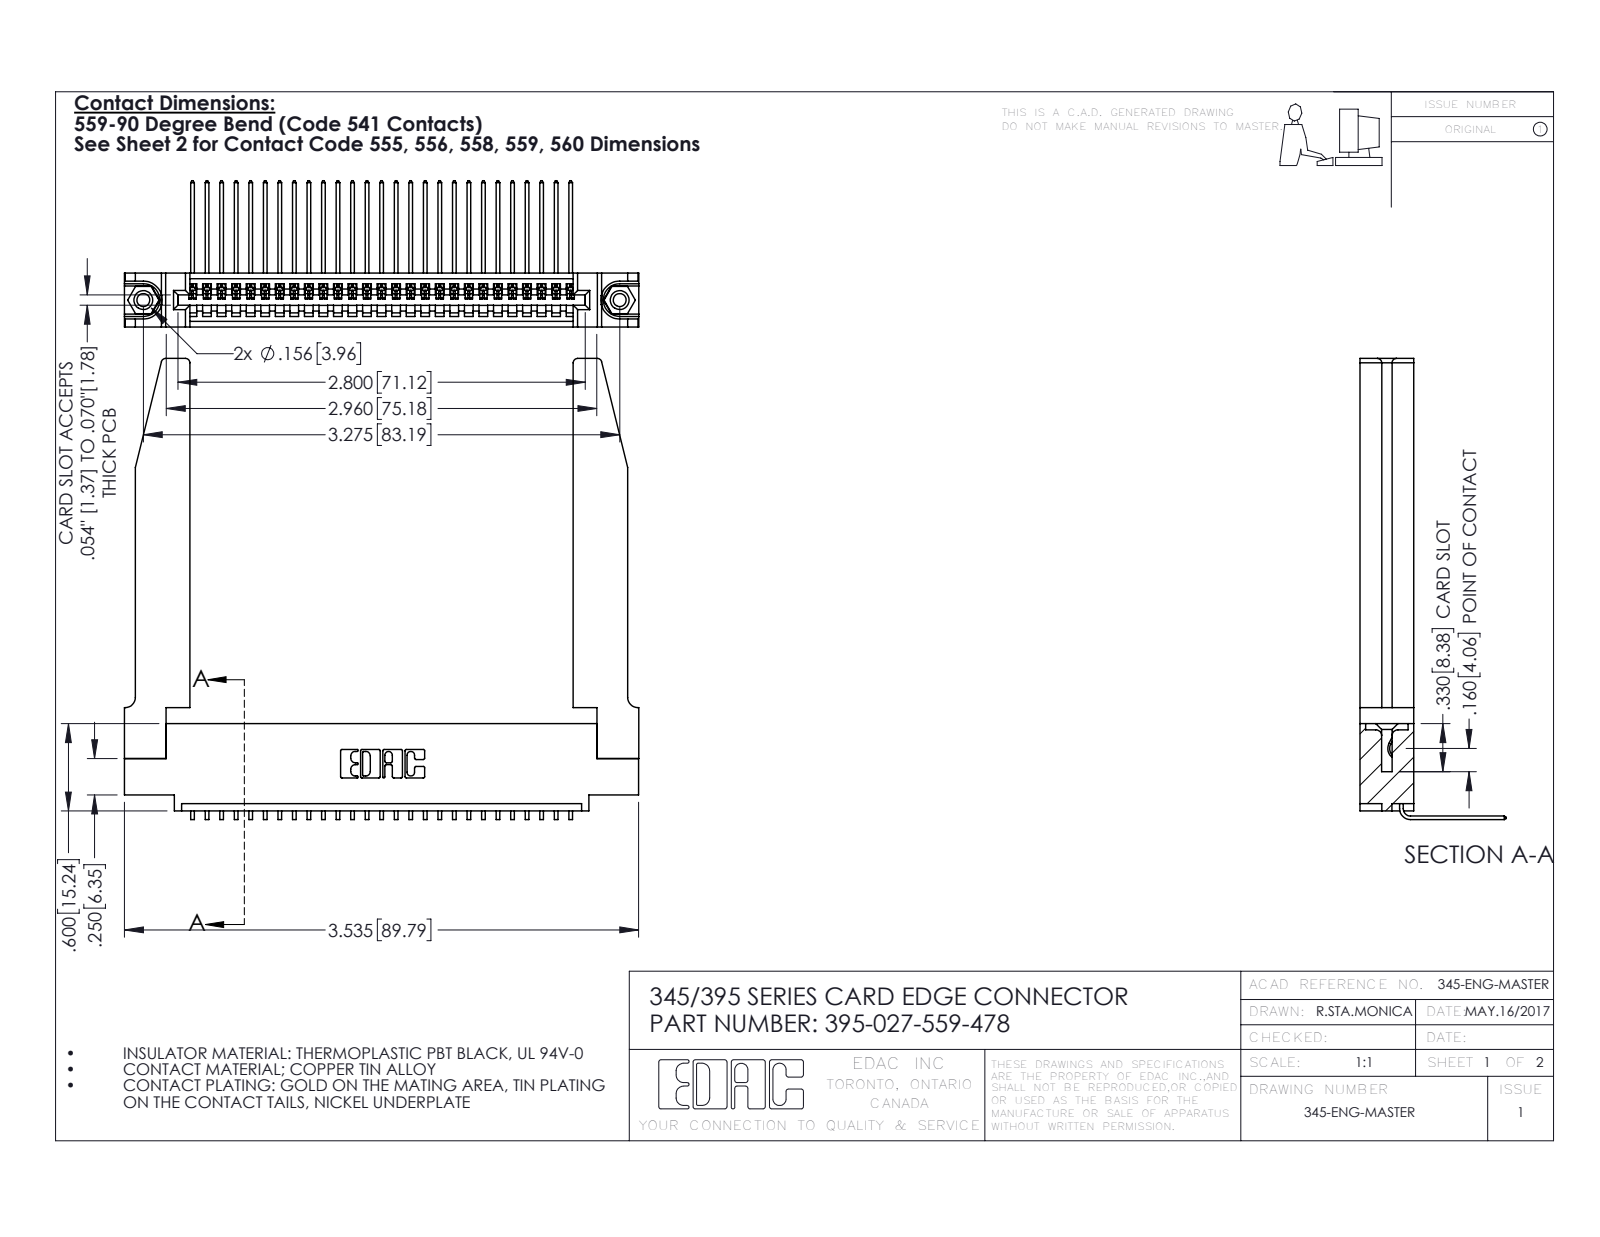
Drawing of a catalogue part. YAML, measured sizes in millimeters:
part_name: "345-292-001_558 559 Tail - 1; 345-250-001_345-250-001-102; 345 Part_0.110 Offset - 0.156 Dia-TH; 345-220-078_345-220-078 (+1 more)"
step_written_by: "SolidWorks 2016 (CONFIG_CONTROL_DESIGN)"
units: millimeters
bodies: {solids: 32, faces: 1984, planar: 1360, cylindrical: 572, other: 52}
overall_size: [89.8, 80.5, 25.5]
volume: 16200
surface_area: 18450
round_holes:
  - {diameter: 2.3, count: 2}
  - {diameter: 3.2, count: 2}
  - {diameter: 4, count: 2}
  - {diameter: 1.6, count: 1}
round_bosses_or_shafts:
  - {diameter: 3.9, count: 2}
partial_cylinders:
  - {radius: 0.2, count: 54}
  - {radius: 0.3, count: 22}
  - {radius: 0.8, count: 8}
  - {radius: 0.2, count: 6}
  - {radius: 0.8, count: 6}
  - {radius: 0.7, count: 3}
  - {radius: 0.8, count: 2}
  - {radius: 1, count: 2}
face_to_face_distances: [9.4, 1.8, 7.6, 5.1, 2.5, 6.9, 0.6, 3.8, 3.8, 5.7]
hole_center_spacings: [6.9, 77.2, 83.2]
